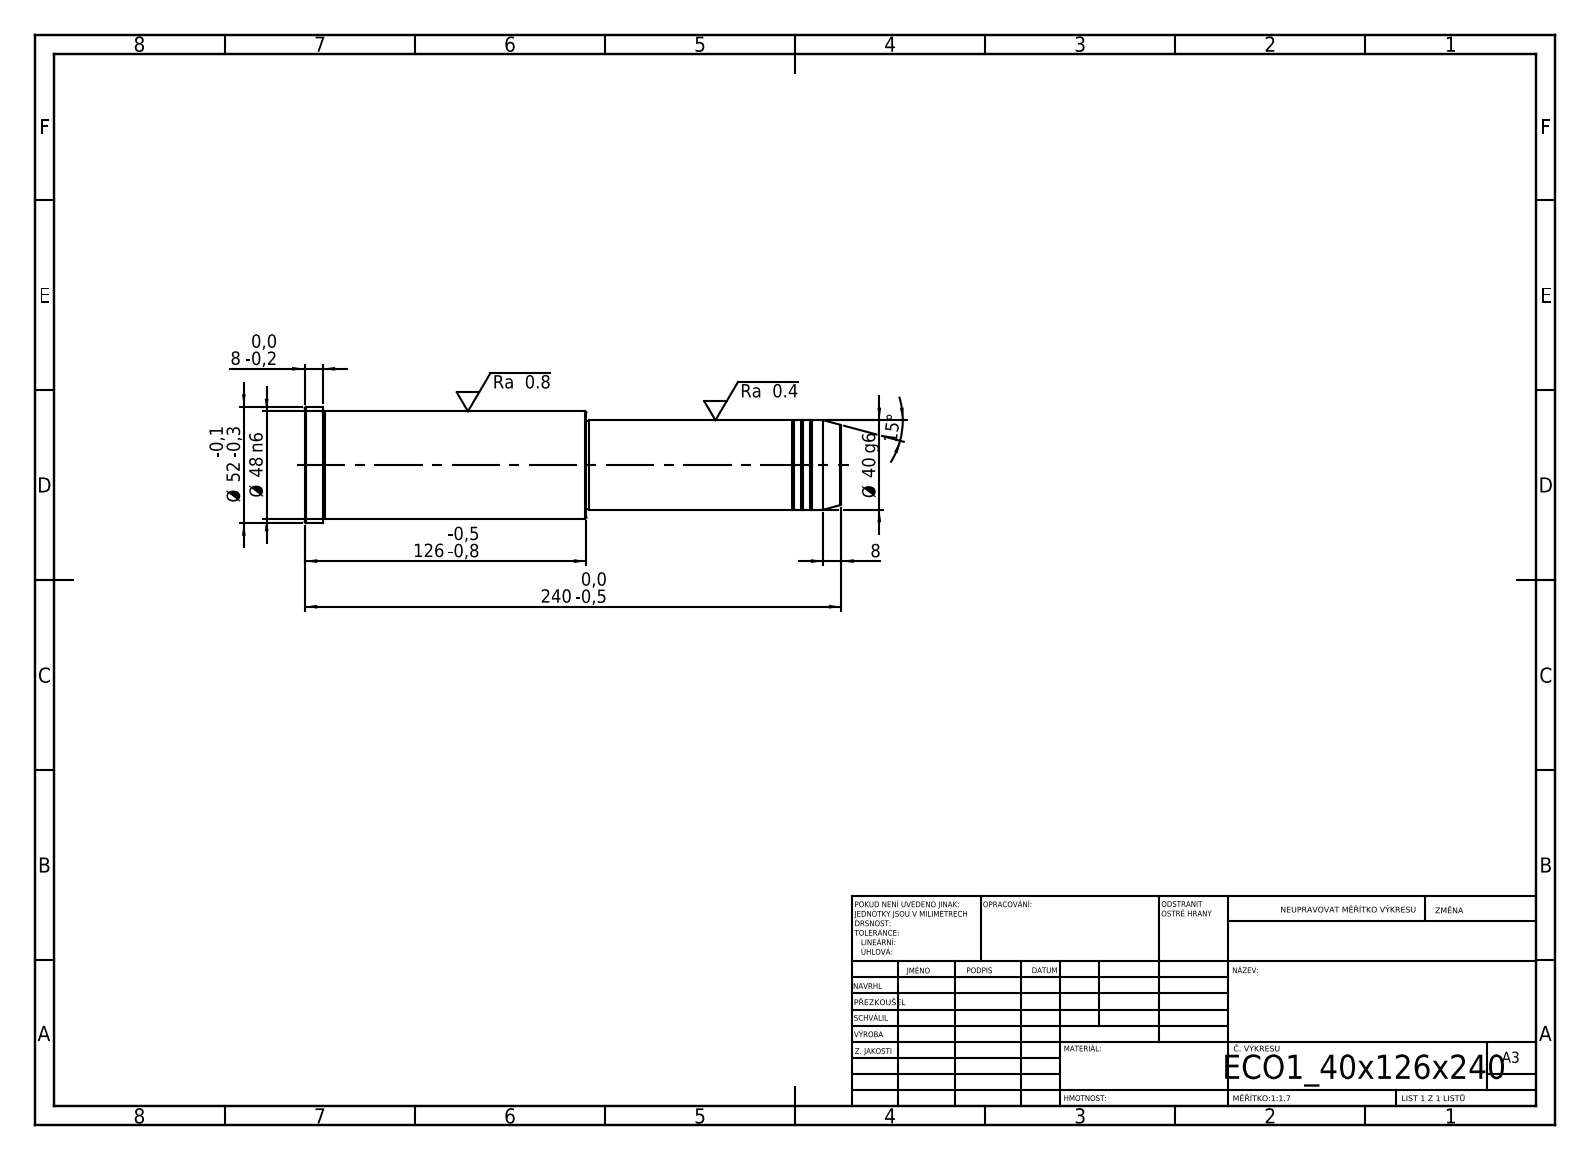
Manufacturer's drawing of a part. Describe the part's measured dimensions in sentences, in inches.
Its 3-D file was written by "SolidWorks 2019 (CONFIG_CONTROL_DESIGN)". It is 1 solid with 43 faces: 5 planar, 14 cylindrical and 24 other. Overall it measures 9.449 by 2.047 by 2.047 inches. Its volume is 22.73 cubic inches and its surface area 58.44 square inches. Round bosses or shafts: 1 of diameter 2.047, 1 of diameter 1.89, 1 of diameter 1.575, 1 of diameter 1.535. The main face-to-face distances are 9.449, 4.488, 4.961, 9.134, 4.646, 0.315, 4.449, 0.039, 4.685, 5.
